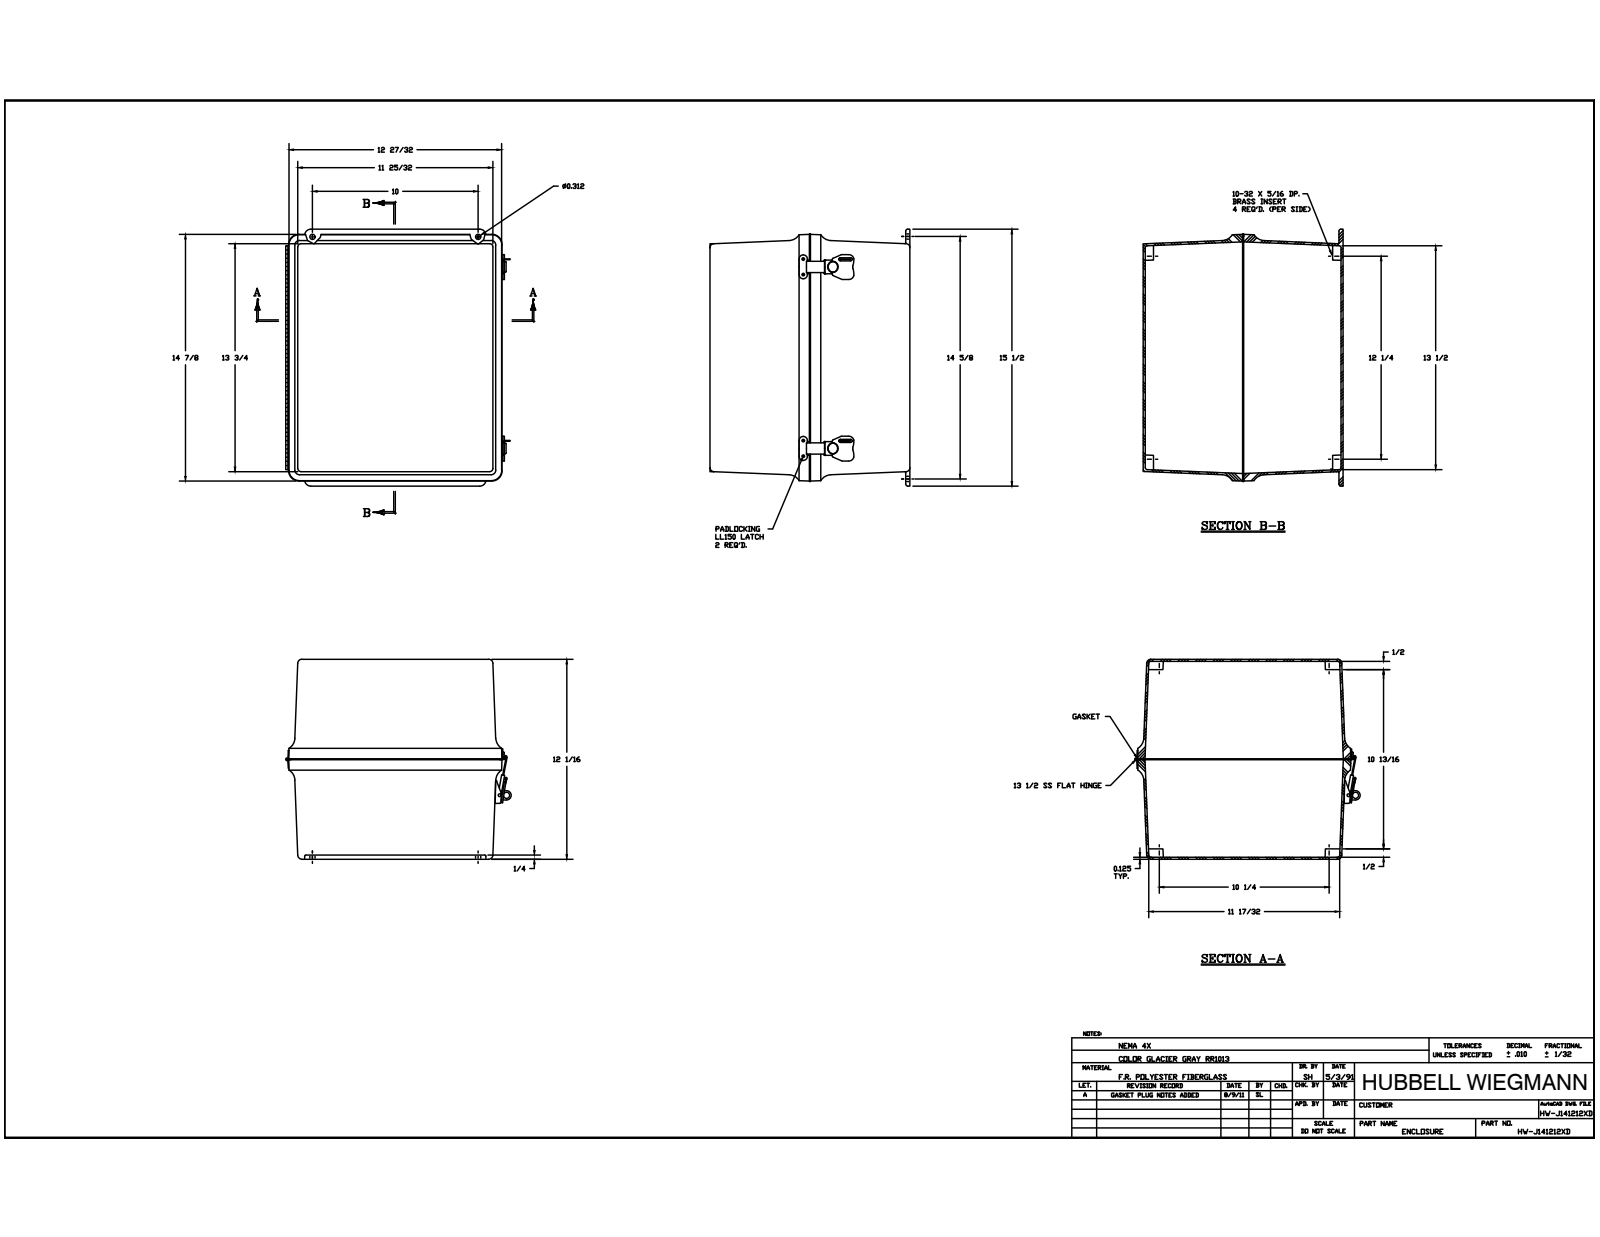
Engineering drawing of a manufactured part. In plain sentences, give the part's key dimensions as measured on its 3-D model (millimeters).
The part is named "J1412HL_2; RMINS45821P_129; RMINS45821P_130; RMINS45821P_131 (+8 more)". Its 3-D file was written by "Autodesk Inventor 2014 (AUTOMOTIVE_DESIGN)". It is 54 solids with 1463 faces: 626 planar, 560 cylindrical and 277 other. Overall it measures 393.7 by 344.24 by 306.21 millimeters. Its volume is 2 476 000 cubic millimeters and its surface area 1 328 000 square millimeters. Round holes: 18 of diameter 3.56, 11 of diameter 3.86, 10 of diameter 3.45, 7 of diameter 3.96, 4 of diameter 3.3, 4 of diameter 4.2, 4 of diameter 5, 4 of diameter 5.54, 2 of diameter 3, 2 of diameter 3.5, 2 of diameter 4.9, 2 of diameter 13.5. Round bosses or shafts: 18 of diameter 6.35, 18 of diameter 3.17, 7 of diameter 6.86, 2 of diameter 14.8, 2 of diameter 13.3, 2 of diameter 5.3, 2 of diameter 4.7, 2 of diameter 3.25. Partial cylindrical surfaces (rounded edges, fillets, slot ends): 52 of radius 0.79, 19 of radius 2, 16 of radius 6.35, 14 of radius 19.05, 12 of radius 3.17, 8 of radius 0.95, 8 of radius 1, 8 of radius 1.15. The main face-to-face distances are 3.17, 3.18, 299.86, 303.76, 306.21, 303.03, 303.04, 354.51, 306.93, 310.11. The hole center spacings are 82.55, 34.8, 165.1, 276.41, 286.01, 336.65, 405.7, 260.35.
